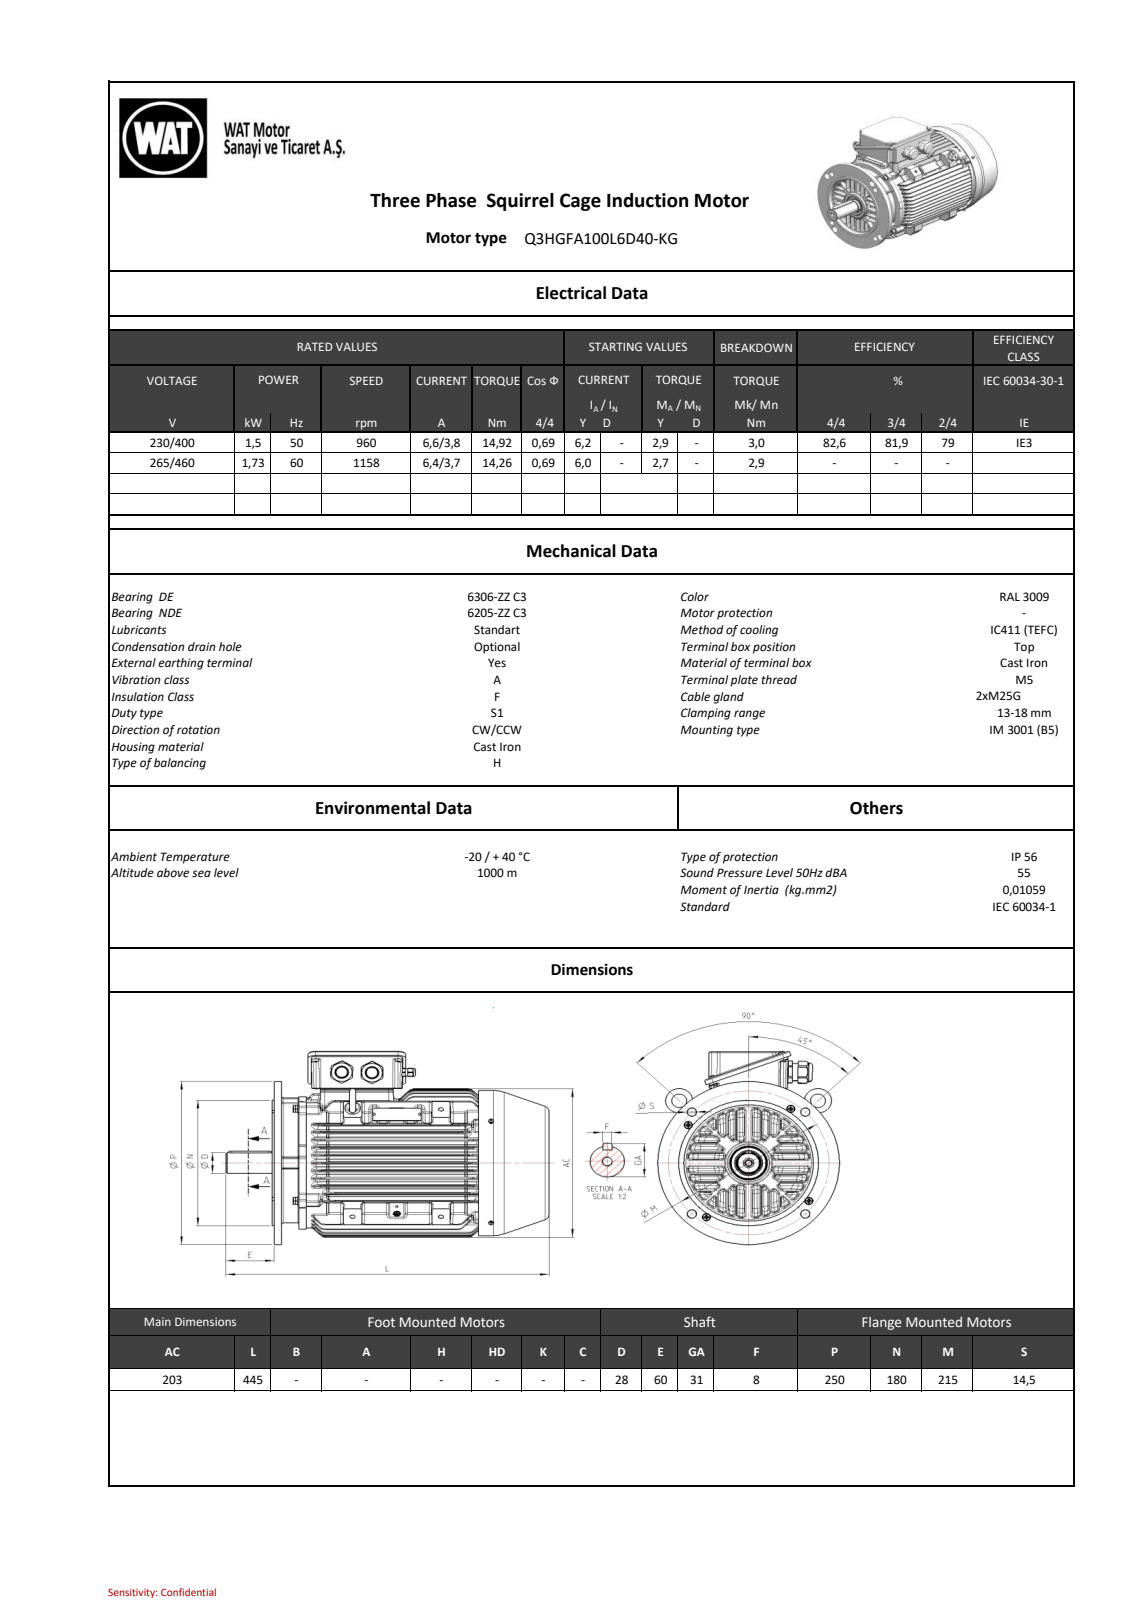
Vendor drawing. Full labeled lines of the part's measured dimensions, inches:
Part name (STEP PRODUCT): C90125944CFF0hne
STEP written by: SIEMENS PLM Software NX 11.0 (AUTOMOTIVE_DESIGN)
Units: inches
Bodies: 0 solids, 3906 faces (767 planar, 942 cylindrical, 2197 other)
Overall size (bounding box): 17.52 × 11.436 × 9.843
Round holes (diameter × count): ⌀0.197 ×9, ⌀0.268 ×6, ⌀0.394 ×6, ⌀0.433 ×4, ⌀0.165 ×2, ⌀0.677 ×2, ⌀0.256 ×1, ⌀0.276 ×1, ⌀0.335 ×1, ⌀0.413 ×1, ⌀0.551 ×1, ⌀1.709 ×1
Round bosses / shafts (diameter × count): ⌀0.341 ×4, ⌀0.315 ×4, ⌀0.157 ×3, ⌀1.091 ×2, ⌀0.994 ×2, ⌀0.787 ×2, ⌀0.472 ×2, ⌀9.843 ×1
Partial cylindrical surfaces — rounded edges, fillets, slot ends (radius × count): R0.157 ×240, R0.059 ×118, R0.118 ×67, R0.079 ×28, R0.039 ×23, R0.01 ×17, R1.043 ×12, R1.358 ×12
Main face-to-face distances: 0.533, 1.069, 0.536, 1.608, 1.075, 0.539, 3.104, 2.567, 2.035, 2.15
Hole centre spacings: 3.524, 4.983, 2.303, 2.815, 1.223, 4.043, 5.118, 5.772
